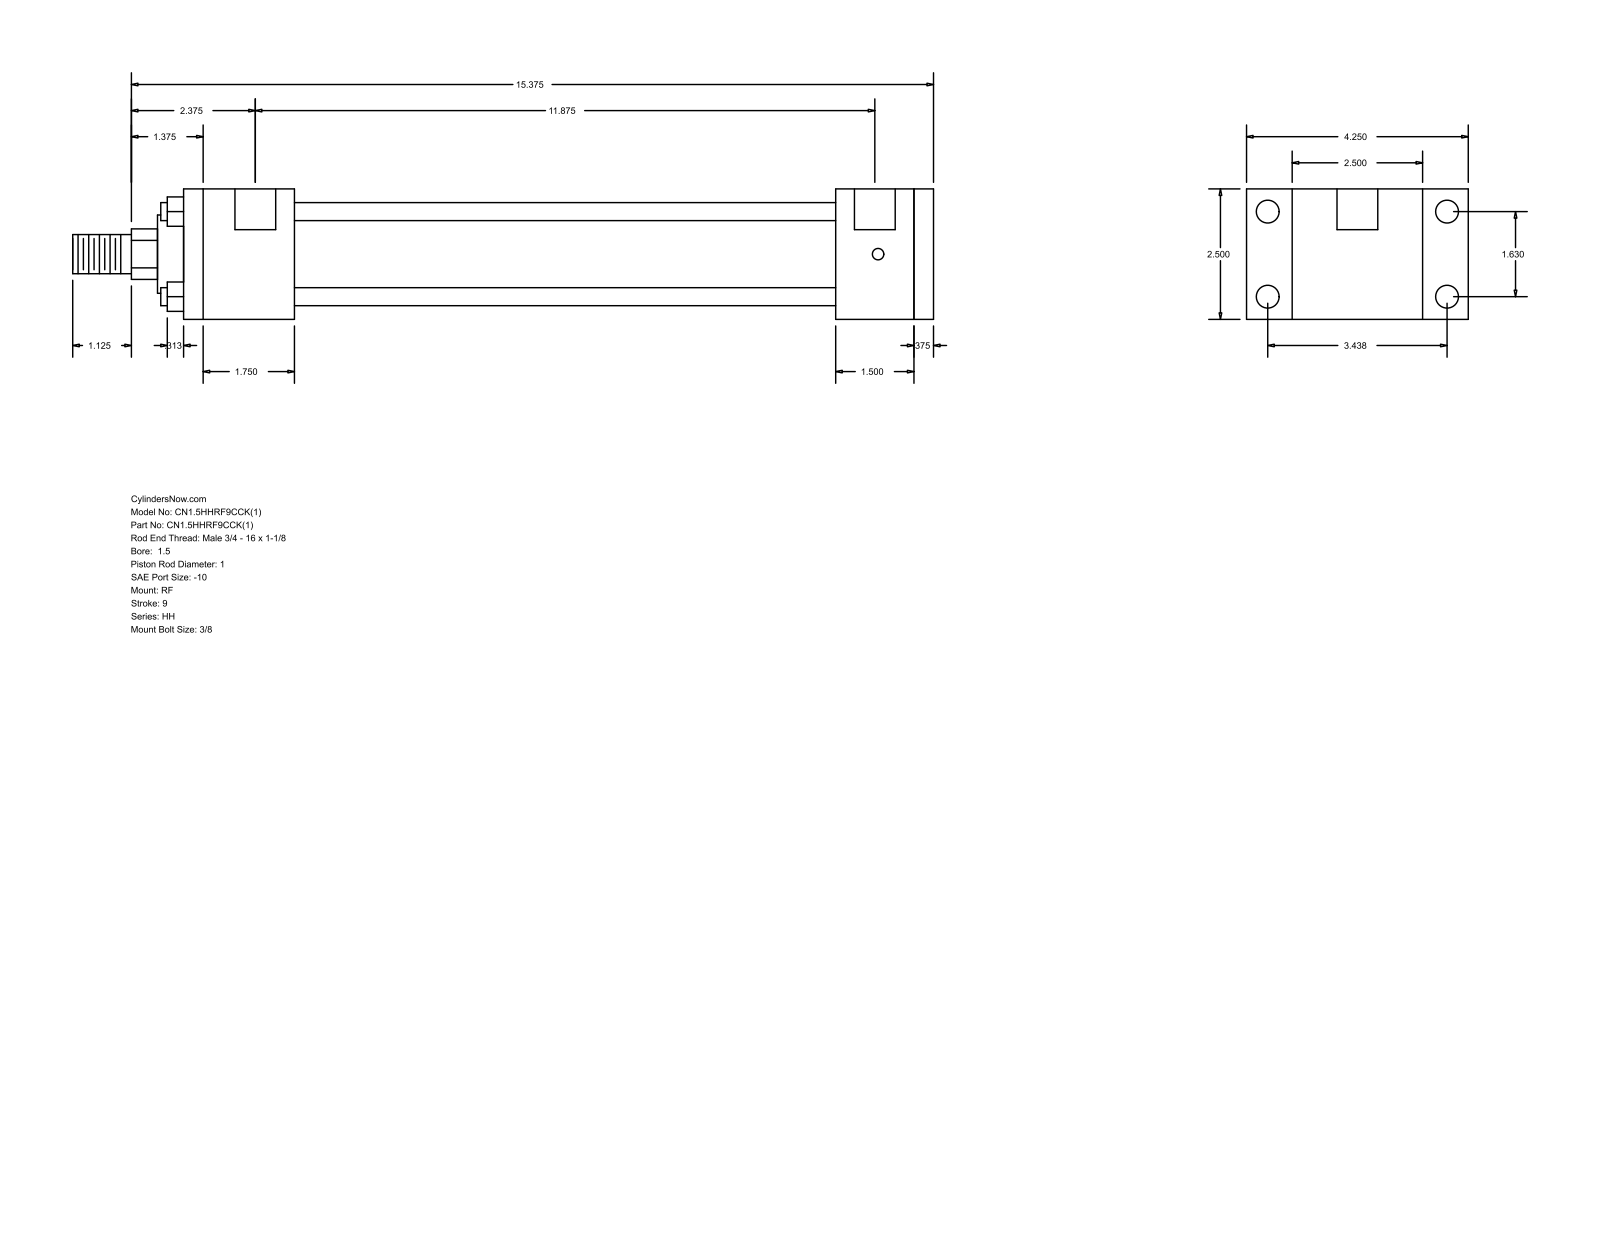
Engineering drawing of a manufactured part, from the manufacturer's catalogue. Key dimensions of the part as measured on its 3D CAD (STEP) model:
Part name (STEP PRODUCT): HH_RF__0150_1
STEP written by: GSSL Pune (CONFIG_CONTROL_DESIGN)
Units: millimetres
Bodies: 0 solids, 92 faces (64 planar, 28 cylindrical, 0 other)
Overall size (bounding box): 419.1 × 107.95 × 63.5
Round holes (diameter × count): ⌀5.56 ×4, ⌀11.13 ×4, ⌀19.84 ×2
Round bosses / shafts (diameter × count): ⌀8.76 ×4, ⌀44.45 ×1, ⌀38.1 ×1, ⌀25.4 ×1, ⌀19.05 ×1
Partial cylindrical surfaces — rounded edges, fillets, slot ends (radius × count): R12.29 ×1
Main face-to-face distances: 63.5, 9.52, 38.1, 263.52, 301.62, 311.14, 47.62, 53.98, 317.5, 355.6
Hole centre spacings: 1.59, 41.4, 87.32, 96.64, 303.21, 304.8, 301.62
